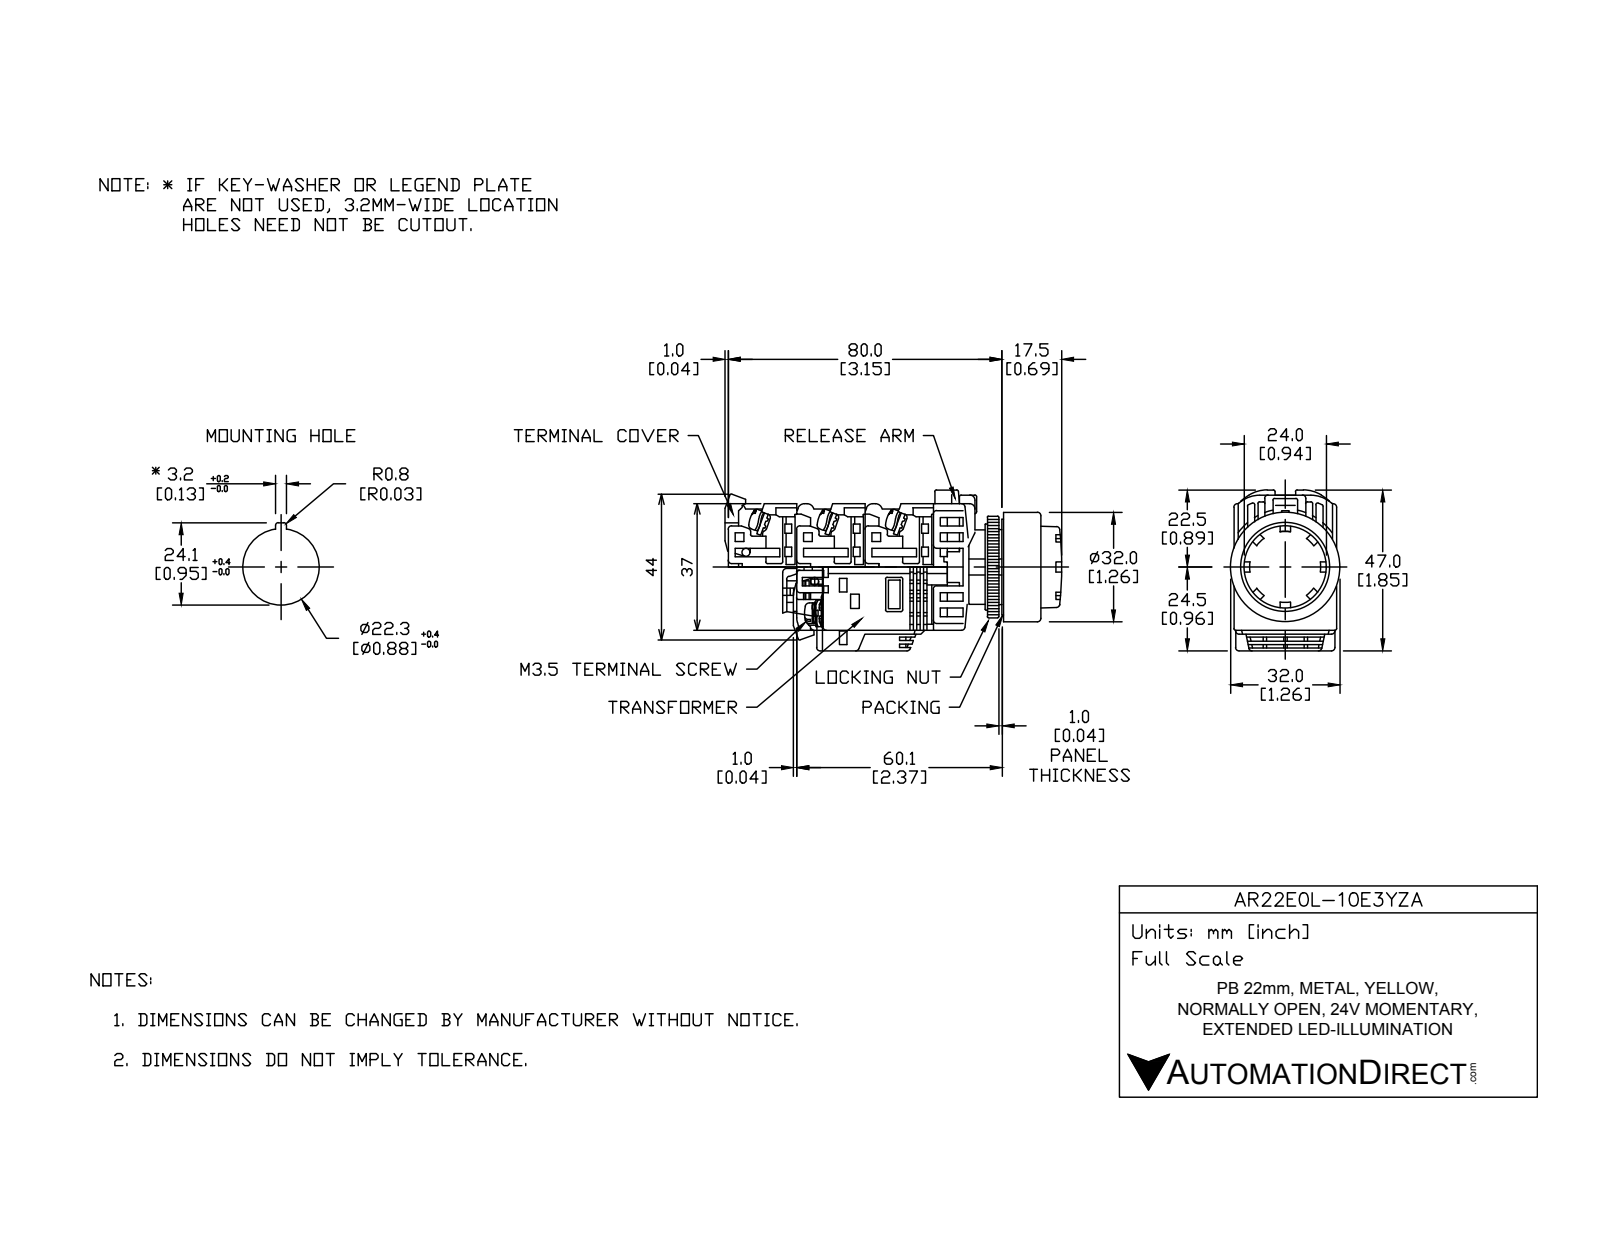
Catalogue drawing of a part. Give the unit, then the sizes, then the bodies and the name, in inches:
Units: inches
Overall size (bounding box): 2.333 × 1.725 × 1.26
Round holes (diameter × count): ⌀0.858 ×1, ⌀0.866 ×1, ⌀0.984 ×1, ⌀1.22 ×1
Round bosses / shafts (diameter × count): ⌀0.197 ×4, ⌀1.26 ×1, ⌀1.201 ×1, ⌀1.173 ×1, ⌀0.945 ×1, ⌀0.937 ×1, ⌀0.856 ×1, ⌀0.669 ×1
Partial cylindrical surfaces — rounded edges, fillets, slot ends (radius × count): R0.02 ×39, R0.069 ×8, R0.197 ×4, R0.157 ×2, R0.653 ×1, R0.693 ×1
Main face-to-face distances: 0.039, 0.709, 1.122, 1.909, 0.787, 1.142, 0.118, 0.079, 0.827, 0.02
Volume: 2.396 in³ · Surface area: 38.05 in²
Bodies: 18 solids, 475 faces (329 planar, 111 cylindrical, 35 other)
Part name (STEP PRODUCT): AR22E0L-10E3YZA
STEP written by: SolidWorks 2017 (AUTOMOTIVE_DESIGN)
